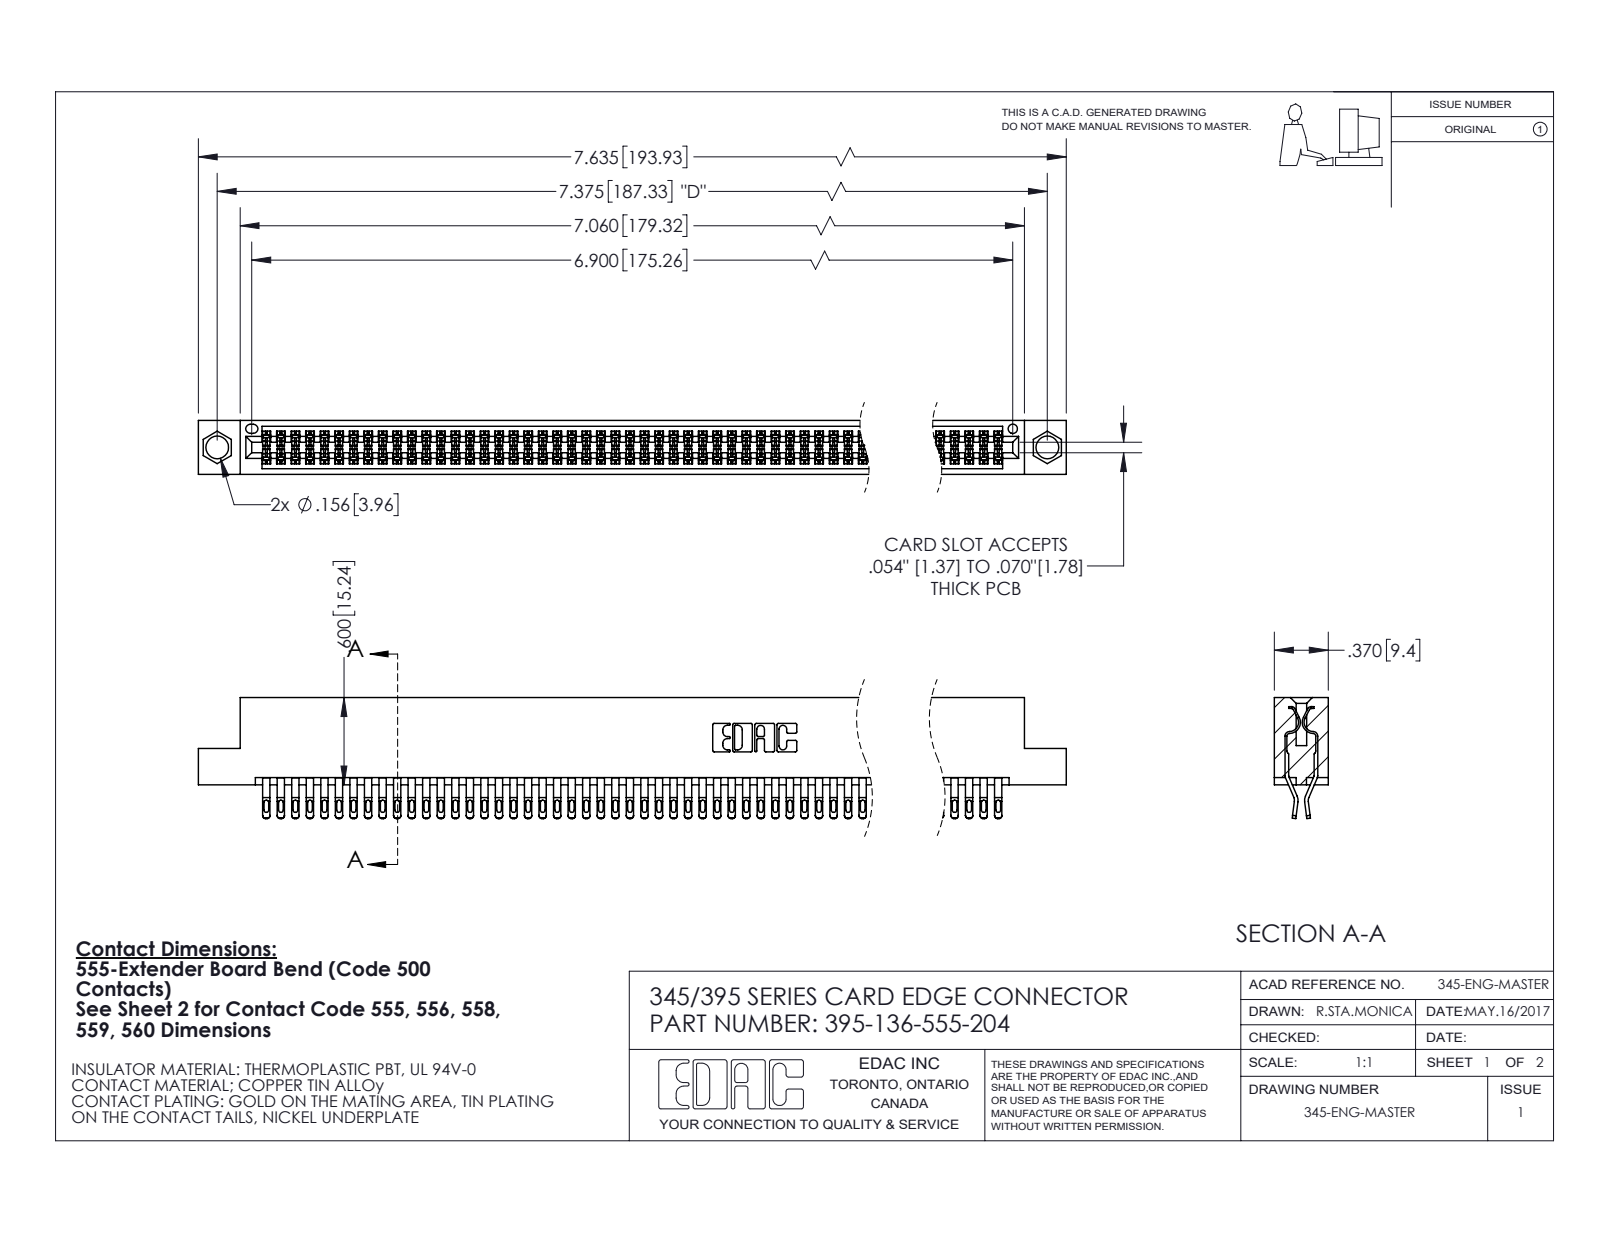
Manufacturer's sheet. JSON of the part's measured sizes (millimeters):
{"part_name": "345 Part_Flush Mounting Lugs - 0.156 Dia-TI; 395-136-555-204; 345-292-001_555 Tail", "step_written_by": "SolidWorks 2020 (CONFIG_CONTROL_DESIGN)", "units": "millimeters", "bodies": {"solids": 137, "faces": 7756, "planar": 4310, "cylindrical": 3446, "other": 0}, "overall_size": [193.9, 21.1, 9.4], "volume_mm3": 19370, "surface_area_mm2": 30350, "round_holes": [[4, 2], [1.6, 1]], "partial_cylinders_radius": [[0.4, 340], [0.2, 272], [0.5, 272], [0.3, 22], [0.2, 6], [0.8, 6], [0.7, 3], [0.3, 2]], "face_to_face_distances": [7.6, 1.8, 0.6, 9.4, 5.1, 2.5, 6.9, 5.7, 4.4, 3.8], "hole_center_spacings": [6.9, 181.3, 187.3]}
